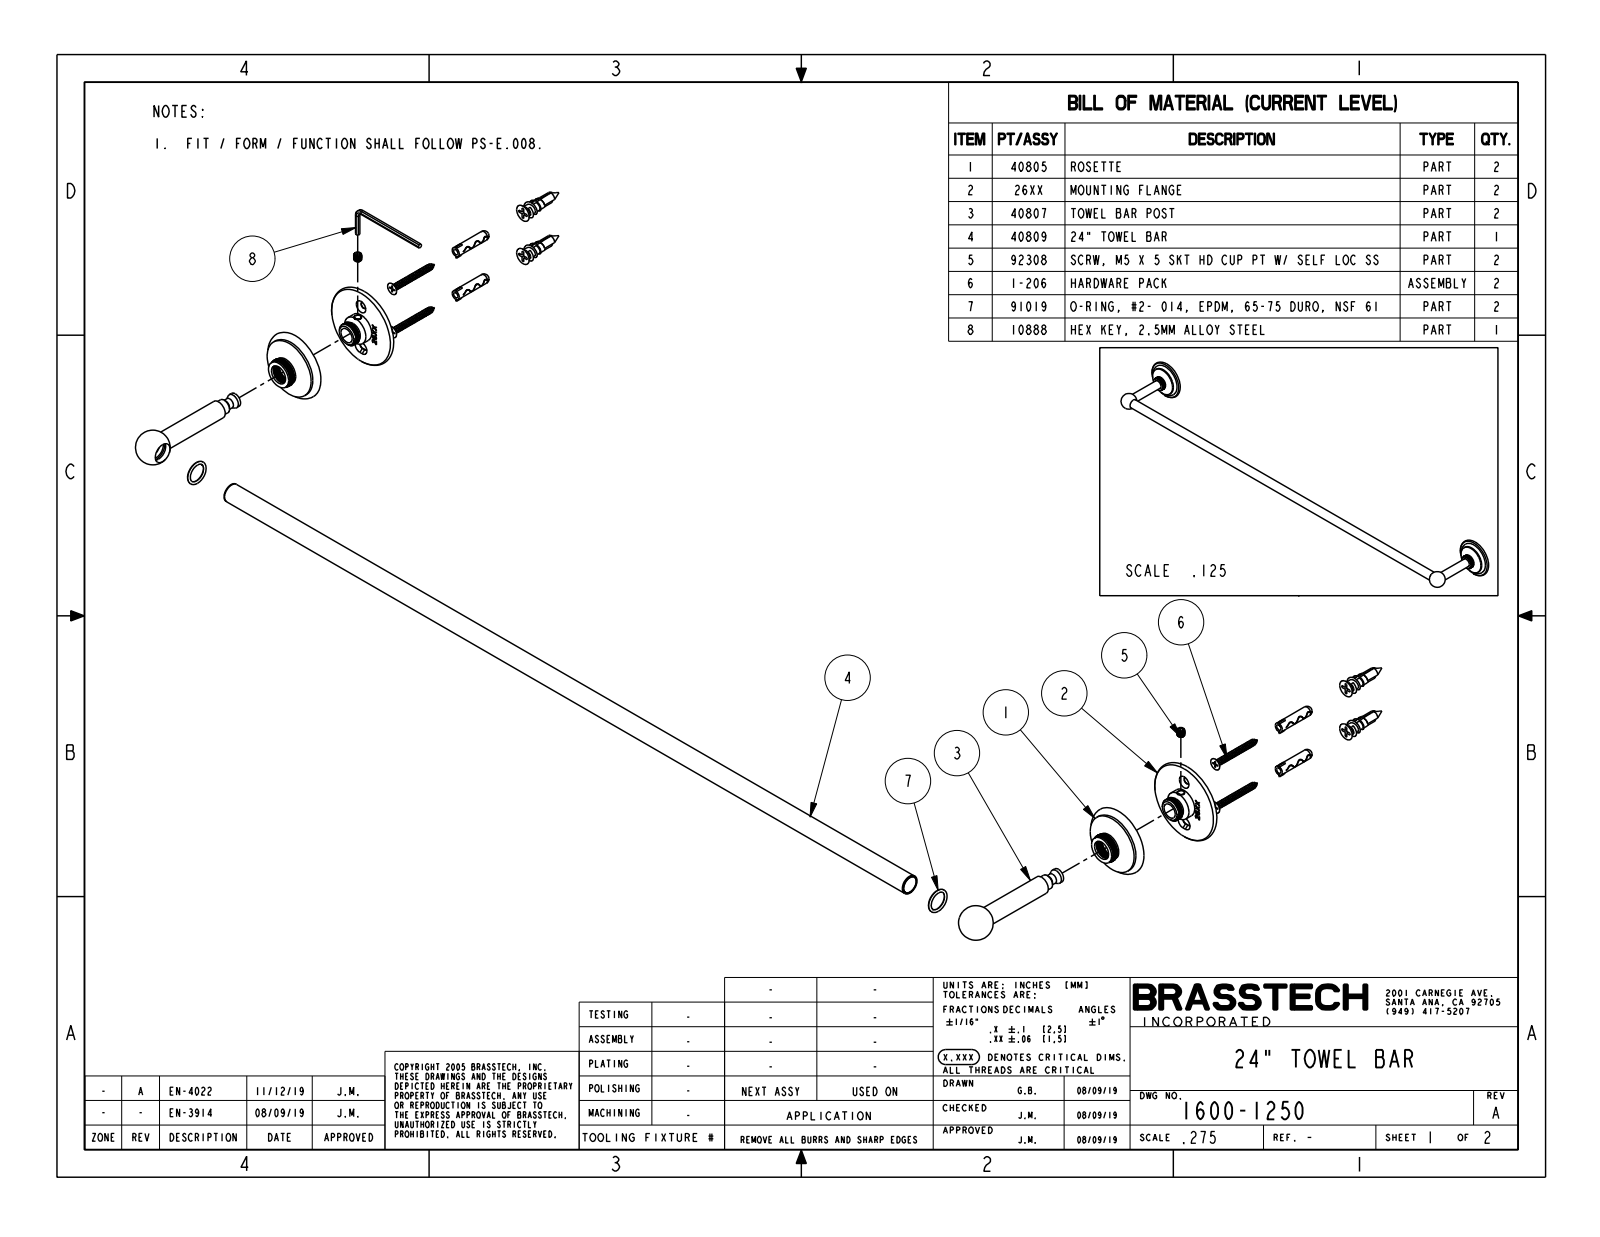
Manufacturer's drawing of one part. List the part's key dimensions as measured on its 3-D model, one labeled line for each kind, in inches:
Part name (STEP PRODUCT): 40805; 26XX; 40807; 40809 (+2 more)
STEP written by: CREO PARAMETRIC BY PTC INC, 2018400 (CONFIG_CONTROL_DESIGN)
Units: inches
Bodies: 9 solids, 1114 faces (628 planar, 178 cylindrical, 308 other)
Overall size (bounding box): 26.111 × 3.386 × 2.126
Volume: 3.711 in³ · Surface area: 182.2 in²
Round holes (diameter × count): ⌀0.157 ×2, ⌀0.165 ×2, ⌀0.177 ×2, ⌀0.197 ×2, ⌀0.394 ×2, ⌀0.496 ×2, ⌀0.555 ×2, ⌀0.62 ×2, ⌀1.583 ×2, ⌀1.89 ×2, ⌀0.437 ×1, ⌀0.52 ×1
Round bosses / shafts (diameter × count): ⌀1.551 ×2, ⌀0.748 ×2, ⌀0.709 ×2, ⌀0.59 ×2, ⌀0.503 ×2, ⌀0.472 ×2, ⌀0.374 ×2, ⌀0.264 ×2
Partial cylindrical surfaces — rounded edges, fillets, slot ends (radius × count): R0.089 ×4
Main face-to-face distances: 0.098, 0.118, 0.02, 0.63, 0.61, 0.512, 0.709, 0.689, 0.591, 0.079
Hole centre spacings: 23.985, 0.625, 23.994
